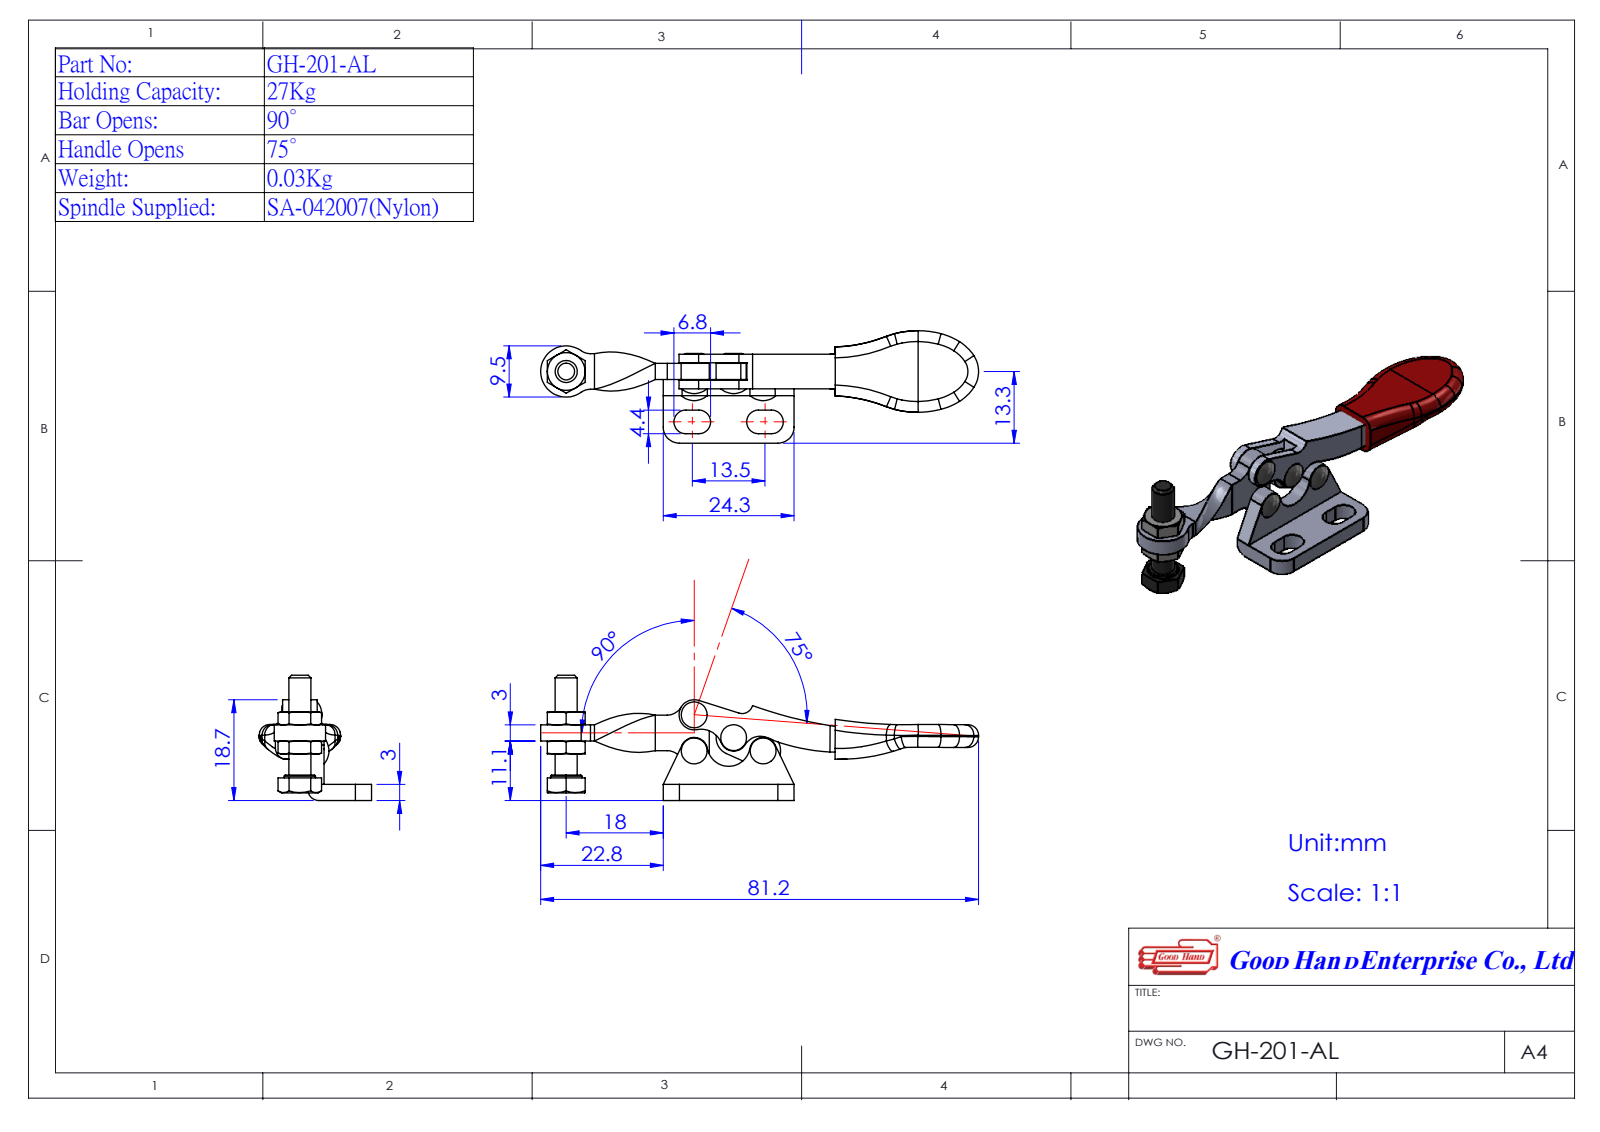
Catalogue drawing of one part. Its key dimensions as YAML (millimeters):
part_name: "1201A08-1^EMC201AL; Group4^EMC201AL; Group5^EMC201AL; EMC201AL (+2 more)"
step_written_by: "SolidWorks 2016 (AUTOMOTIVE_DESIGN)"
units: millimeters
bodies: {solids: 4, faces: 225, planar: 72, cylindrical: 92, other: 61}
overall_size: [81.21, 23.26, 20.77]
volume: 2520
surface_area: 4816
round_holes:
  - {diameter: 2.5, count: 4}
  - {diameter: 4.3, count: 1}
round_bosses_or_shafts:
  - {diameter: 5.8, count: 1}
  - {diameter: 4.1, count: 1}
partial_cylinders:
  - {radius: 3, count: 6}
  - {radius: 2.2, count: 4}
  - {radius: 12.23, count: 4}
  - {radius: 2.5, count: 2}
  - {radius: 2.8, count: 2}
  - {radius: 3.25, count: 2}
  - {radius: 4, count: 2}
  - {radius: 8.67, count: 2}
face_to_face_distances: [3, 1.7, 4.7, 11.05, 4.8, 4.04, 1.6, 3.1, 6.4, 7.7]
hole_center_spacings: [6, 6.7, 7.73, 8.47, 12.8, 14.45]
